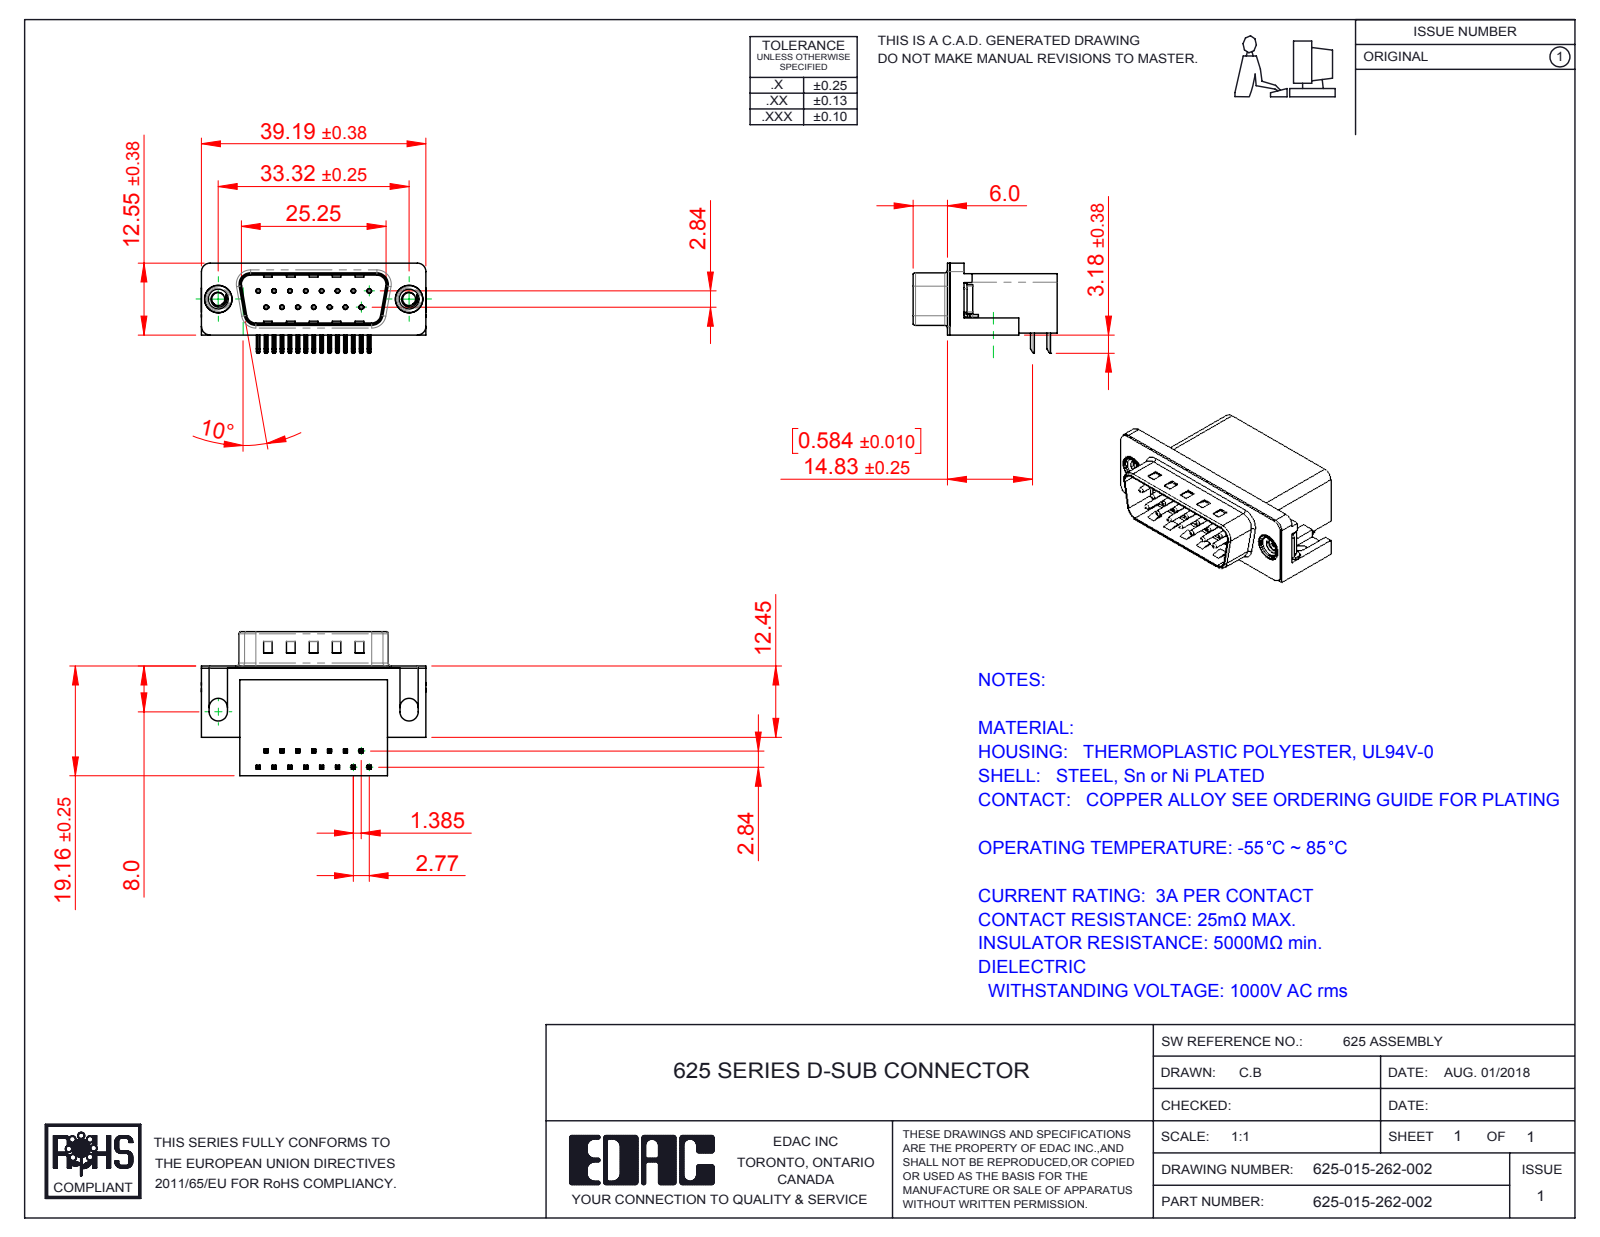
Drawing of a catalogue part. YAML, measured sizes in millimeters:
part_name: "625 Contact Bottom; 625-015-262-002; 625 4-40 Threaded Rivet; 625 Non Board Mount (+3 more)"
step_written_by: "SolidWorks 2016 (CONFIG_CONTROL_DESIGN)"
units: millimeters
bodies: {solids: 21, faces: 1477, planar: 895, cylindrical: 443, other: 139}
overall_size: [39.22, 25.16, 15.73]
volume: 6216
surface_area: 6291
round_holes:
  - {diameter: 0.35, count: 15}
  - {diameter: 0.8, count: 15}
  - {diameter: 2.26, count: 2}
  - {diameter: 4, count: 2}
  - {diameter: 4.8, count: 2}
  - {diameter: 5, count: 2}
round_bosses_or_shafts:
  - {diameter: 0.75, count: 15}
  - {diameter: 4.9, count: 2}
  - {diameter: 4.75, count: 2}
  - {diameter: 3.9, count: 2}
partial_cylinders:
  - {radius: 0.25, count: 68}
  - {radius: 0.12, count: 30}
  - {radius: 1, count: 16}
  - {radius: 0.5, count: 9}
  - {radius: 1.6, count: 8}
  - {radius: 1.5, count: 6}
  - {radius: 0.9, count: 4}
  - {radius: 2, count: 4}
face_to_face_distances: [0.4, 10.35, 18.76, 2.1, 10.46, 19.16, 1.7, 10.86, 8.76, 16.26]
hole_center_spacings: [3.16, 2.77, 5.54, 8.31, 11.08, 5.03, 5.04, 7.48]
